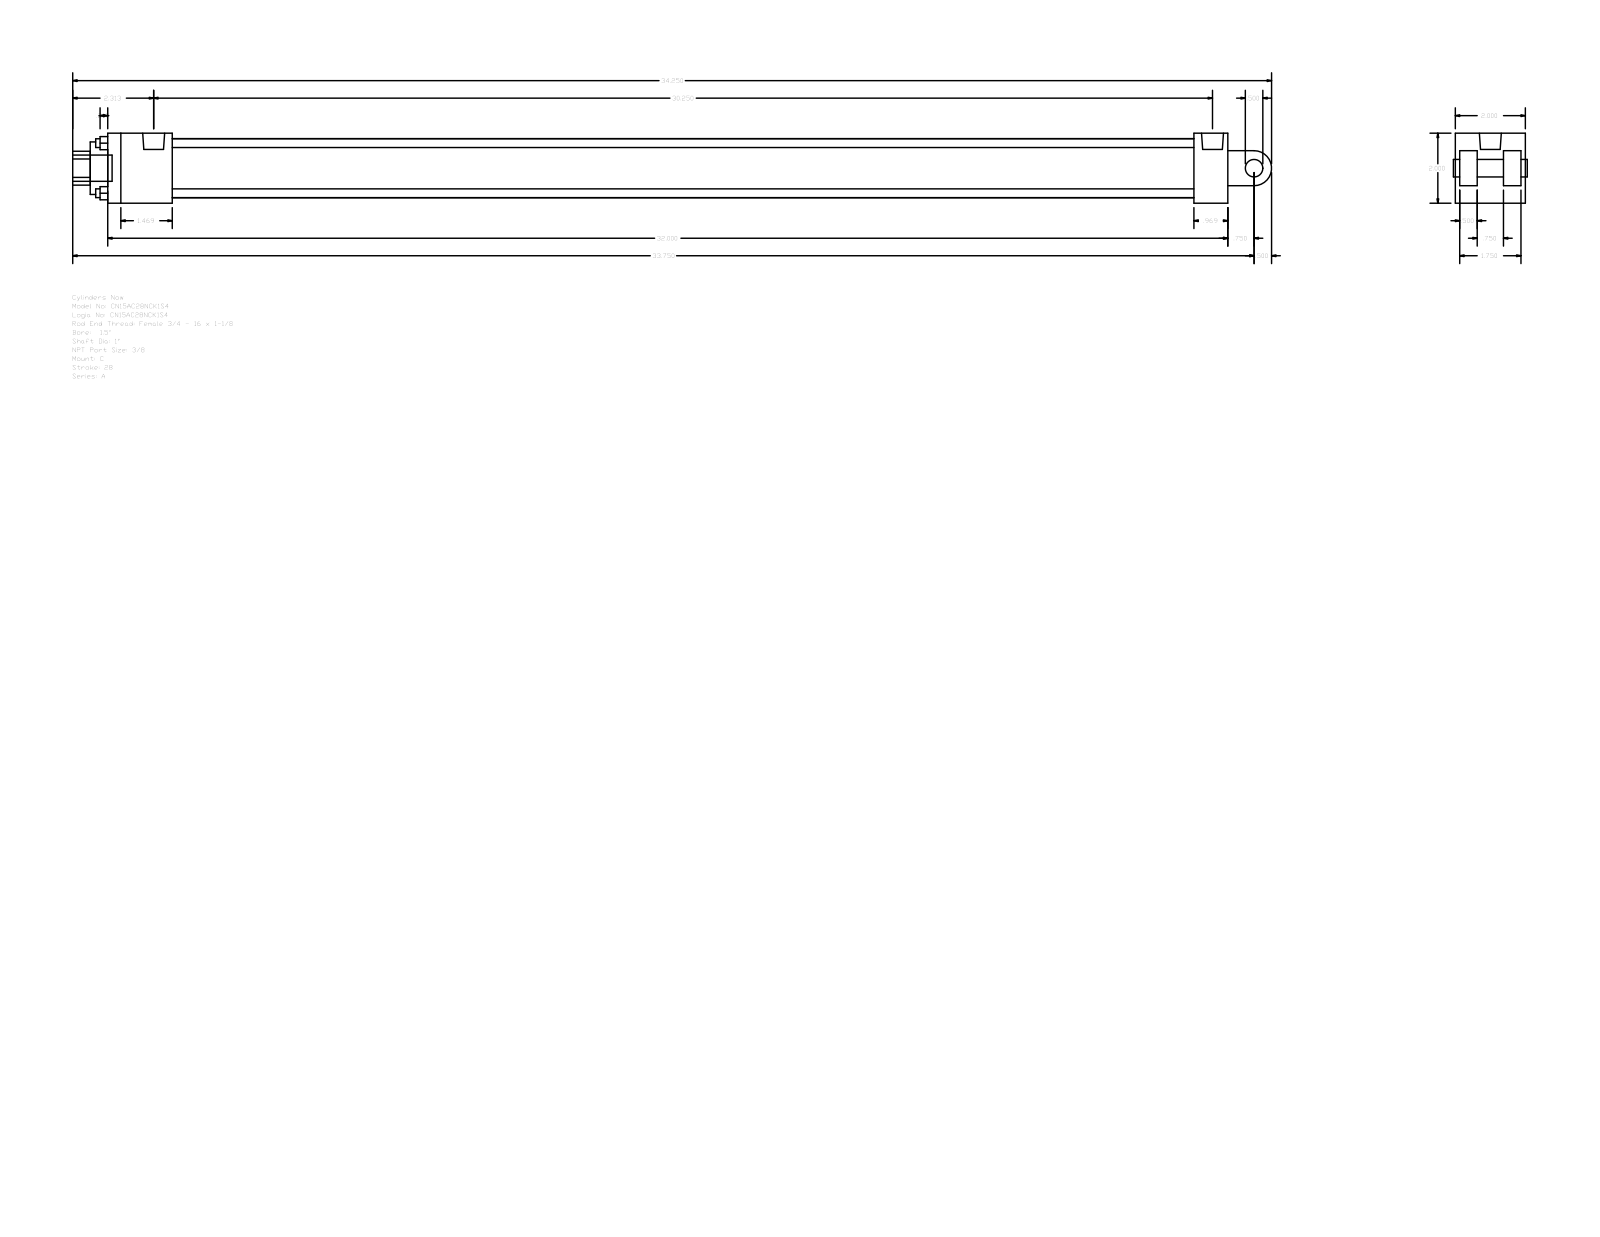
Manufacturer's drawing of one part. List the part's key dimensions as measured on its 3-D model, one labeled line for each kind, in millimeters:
Part name (STEP PRODUCT): A_C__0150_1
STEP written by: GSSL Pune (CONFIG_CONTROL_DESIGN)
Units: millimetres
Bodies: 0 solids, 99 faces (70 planar, 29 cylindrical, 0 other)
Overall size (bounding box): 869.95 × 50.8 × 50.8
Round holes (diameter × count): ⌀6.35 ×4, ⌀5.56 ×2, ⌀15.93 ×1, ⌀25.4 ×1, ⌀38.1 ×1, ⌀42.93 ×1
Round bosses / shafts (diameter × count): ⌀5.56 ×2, ⌀19.05 ×1, ⌀15.93 ×1, ⌀12.7 ×1
Partial cylindrical surfaces — rounded edges, fillets, slot ends (radius × count): R12.29 ×1, R12.7 ×1
Main face-to-face distances: 50.8, 12.7, 3.17, 15.87, 47.63, 34.93, 31.76, 812.8, 788.19, 24.61
Hole centre spacings: 25.68, 36.32, 51.36, 3.97
